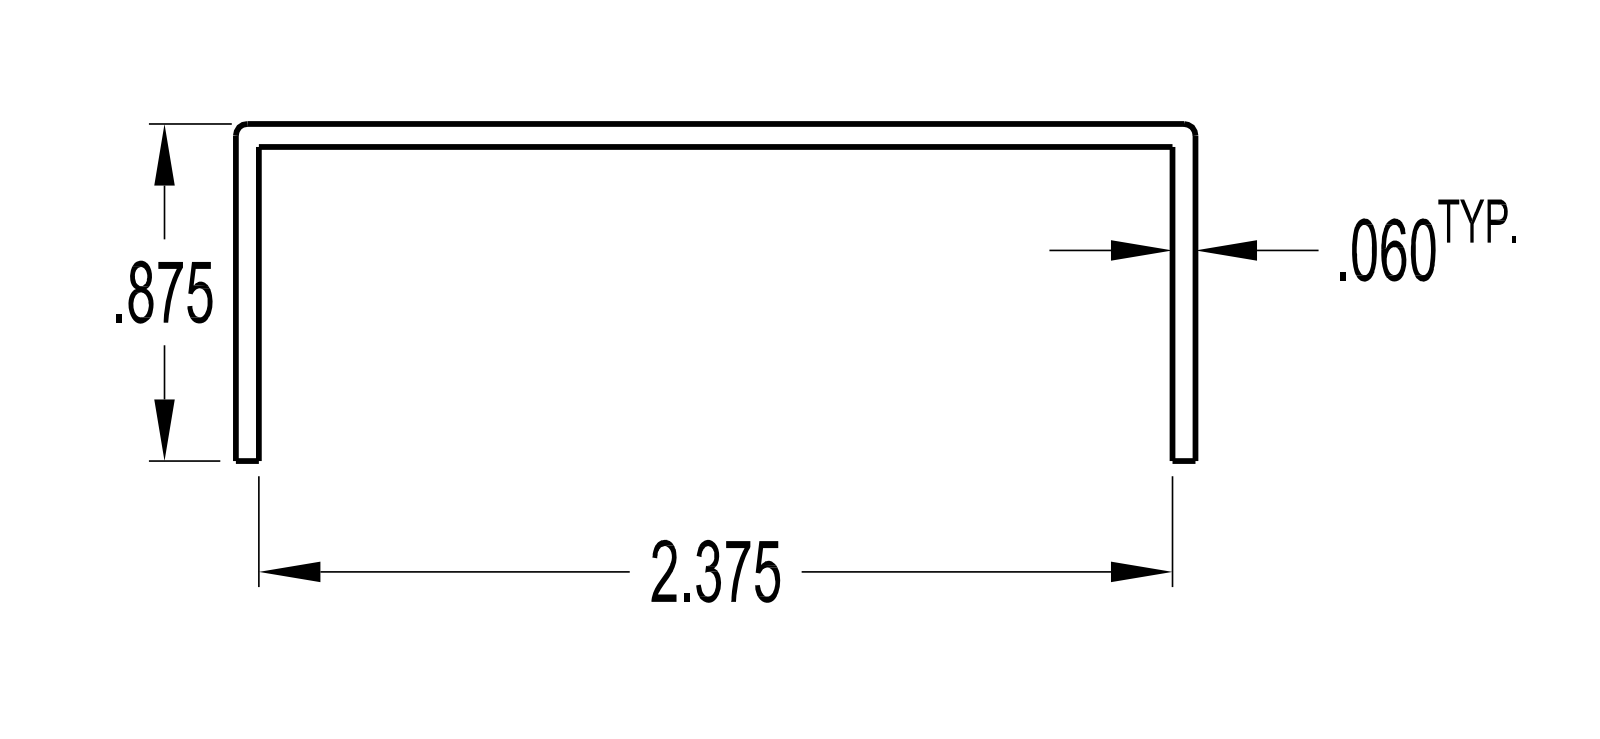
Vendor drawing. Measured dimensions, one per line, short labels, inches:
written by: KeyCreator Pro (AUTOMOTIVE_DESIGN)
unit: in
bodies: 1 solid, 12 faces (10 planar, 2 cylindrical, 0 other)
size: 6 × 2.495 × 0.875
volume: 1.483 in³; area: 50.56 in²
rounds: 2× R0.03
face distances: 0.06, 0.06, 2.435, 2.495, 2.375, 0.815, 0.875, 6
